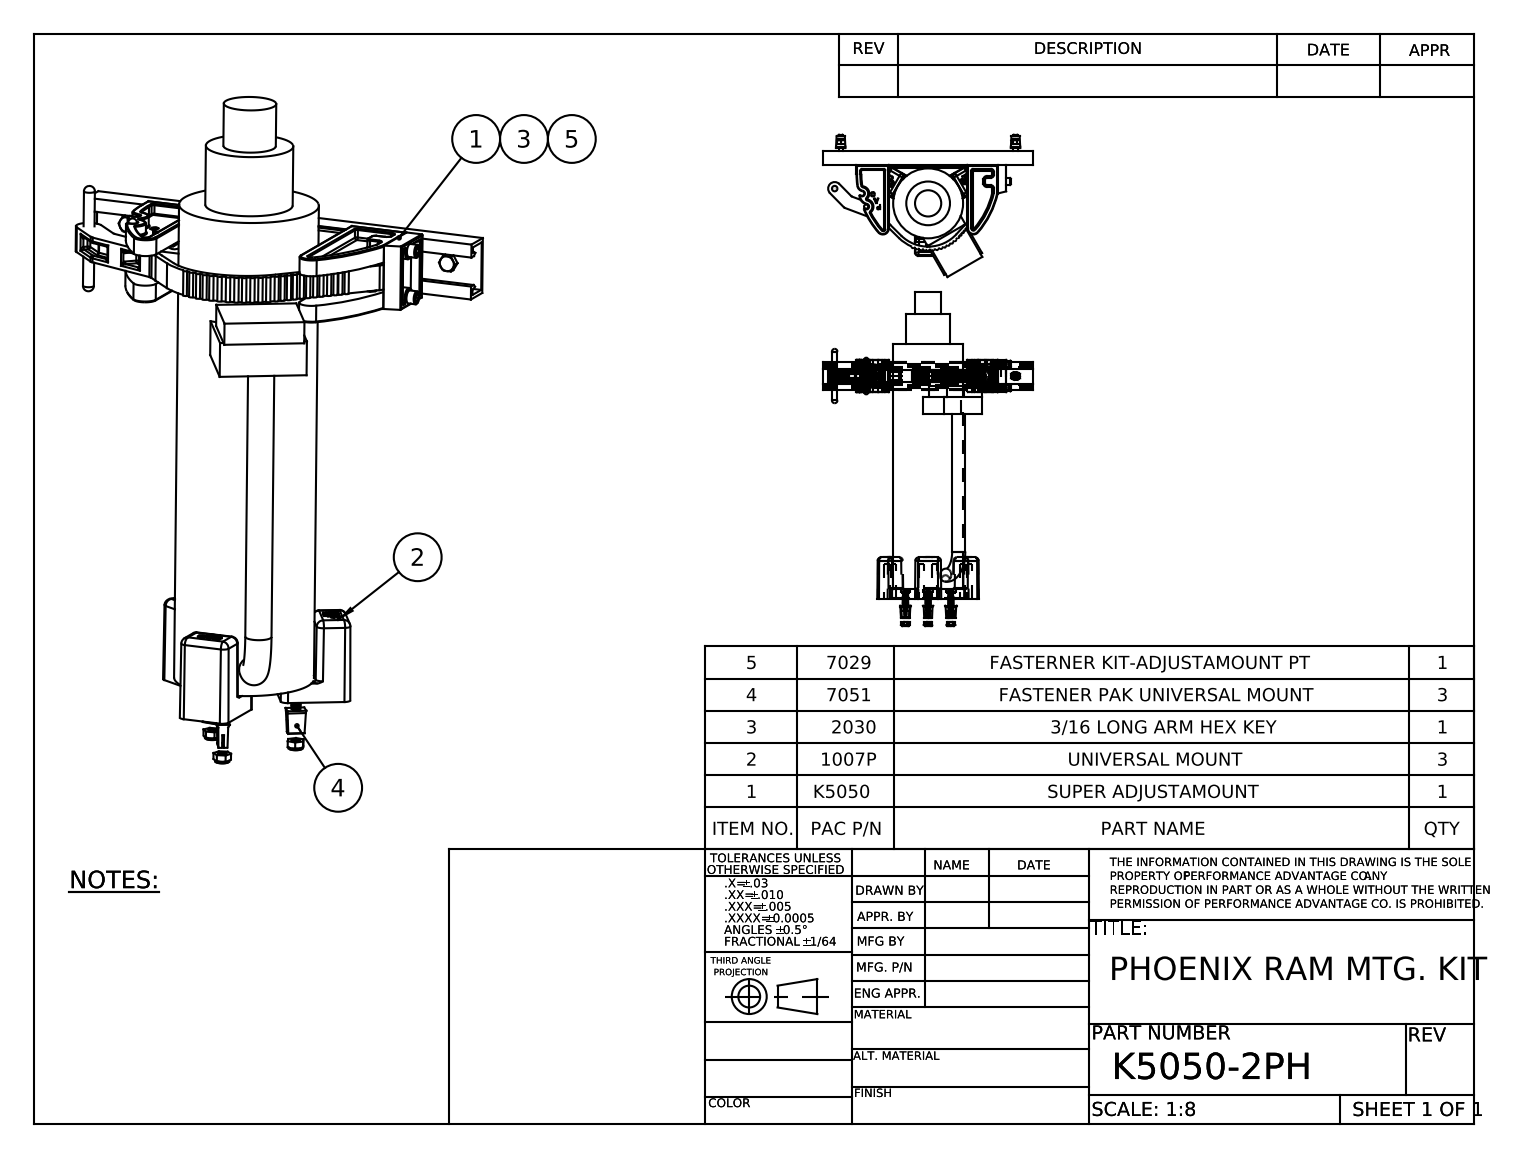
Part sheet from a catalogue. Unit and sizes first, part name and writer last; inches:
Units: inches
Overall size (bounding box): 19.124 × 12 × 8.135
Round holes (diameter × count): ⌀0.313 ×11, ⌀0.201 ×9, ⌀0.269 ×5, ⌀0.206 ×3, ⌀0.26 ×3, ⌀0.531 ×3, ⌀0.687 ×3, ⌀0.25 ×2, ⌀0.266 ×2, ⌀0.288 ×2
Round bosses / shafts (diameter × count): ⌀0.25 ×8, ⌀0.375 ×7, ⌀0.404 ×5, ⌀0.187 ×5, ⌀0.46 ×3, ⌀0.437 ×3, ⌀0.625 ×2, ⌀0.375 ×2
Partial cylindrical surfaces — rounded edges, fillets, slot ends (radius × count): R0.062 ×51, R0.031 ×32, R0.063 ×25, R0.015 ×16, R0.062 ×12, R0.187 ×9, R0.188 ×9, R0.03 ×8
Main face-to-face distances: 1.25, 0.375, 0.188, 0.813, 0.078, 1.75, 0.735, 0.25, 0.266, 0.109
Hole centre spacings: 3.102, 3.803, 0.576, 4.14, 1.064, 3.382, 3.66, 4.379
Volume: 233.2 in³ · Surface area: 632 in²
Bodies: 48 solids, 2941 faces (900 planar, 674 cylindrical, 1367 other)
Part name (STEP PRODUCT): 2011; 2035_10" apart; 2075; 2002_HX-SHCS 0.25-20x0.75x0.75-N (+8 more)
STEP written by: SolidWorks 2014 (CONFIG_CONTROL_DESIGN)
